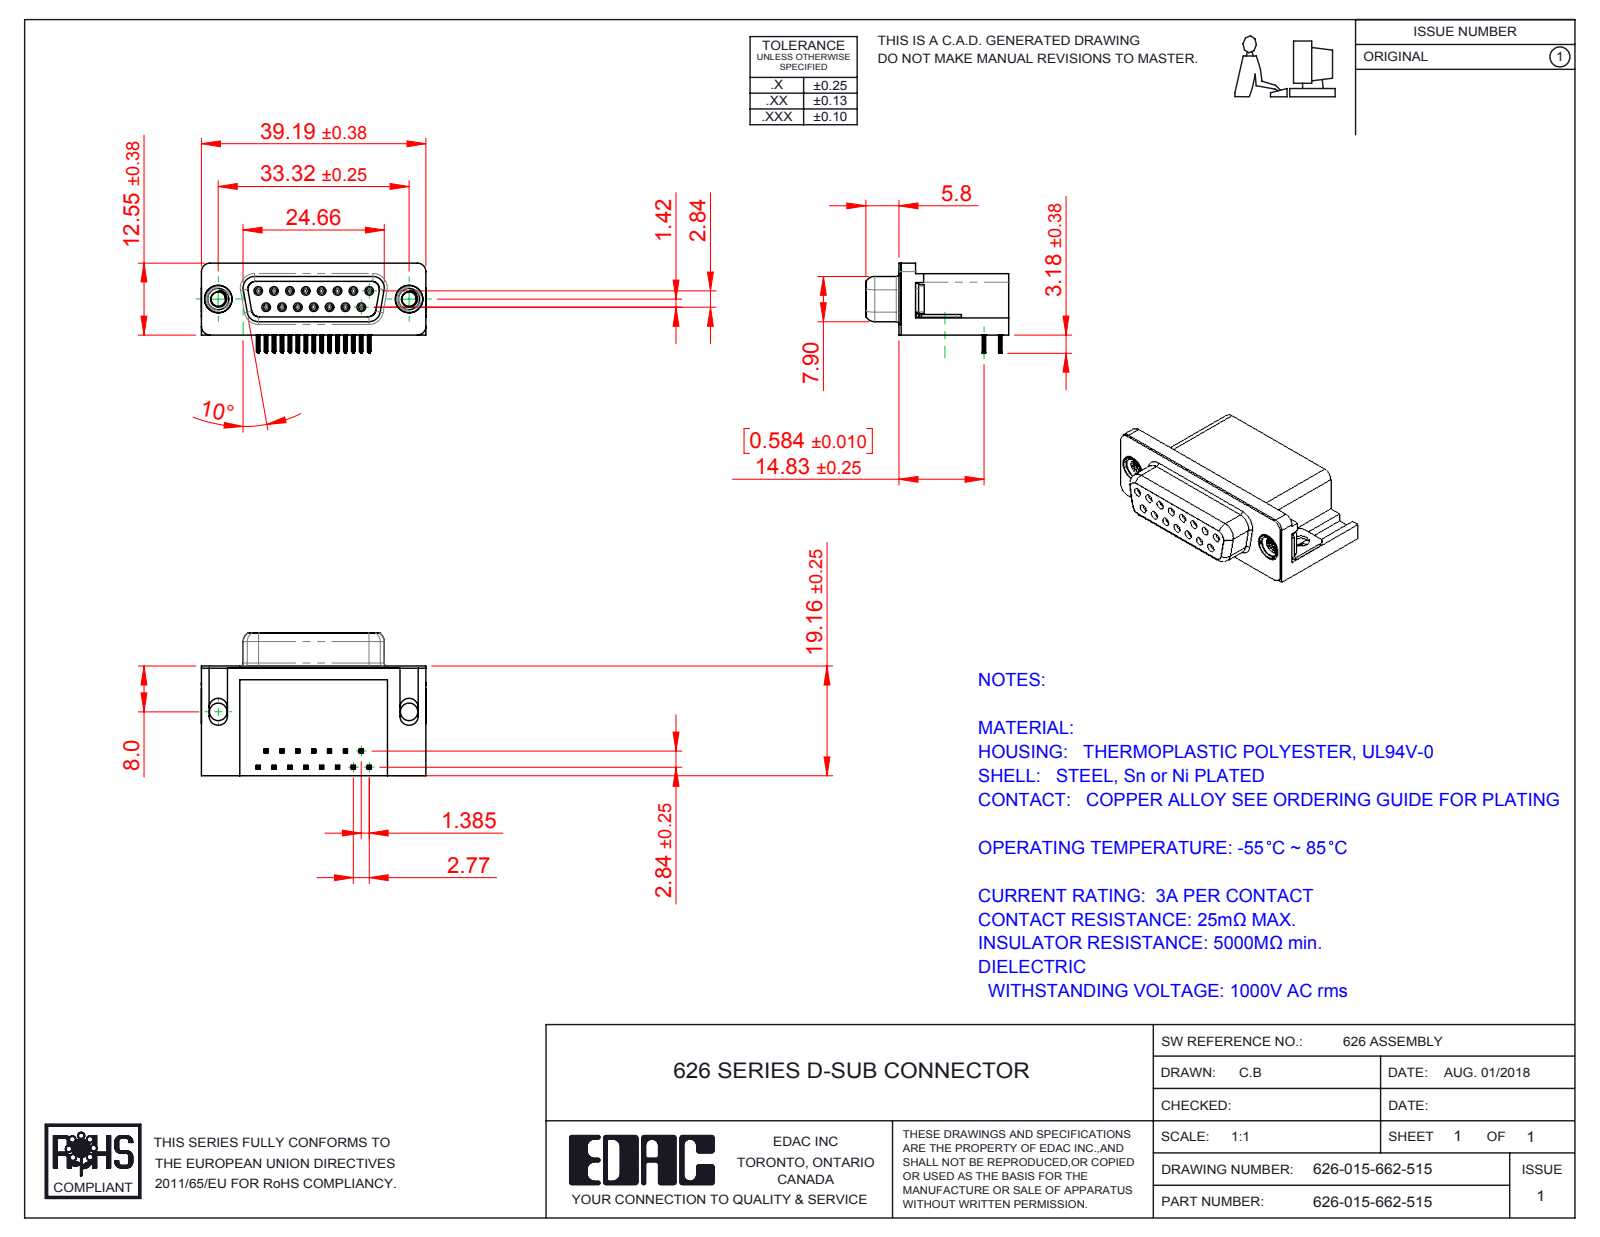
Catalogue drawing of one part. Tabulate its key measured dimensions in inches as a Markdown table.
| quantity | value |
| --- | --- |
| part name | 626 Contact Bottom; 626-015-662-515; 626 M3 Threaded Rivet; 626 Contact Top (+3 more) |
| STEP written by | SolidWorks 2016 (CONFIG_CONTROL_DESIGN) |
| units | inches |
| bodies | 21 solids, 2425 faces (1072 planar, 609 cylindrical, 744 other) |
| overall size | 1.544 × 0.983 × 0.619 |
| volume | 0.442 in³ |
| surface area | 12.43 in² |
| round holes (diameter × count) | 0.031 × 15, 0.035 × 15, 0.098 × 2, 0.12 × 2, 0.157 × 2, 0.189 × 2, 0.197 × 2 |
| round bosses / shafts (diameter × count) | 0.047 × 15, 0.193 × 2, 0.187 × 2, 0.154 × 2 |
| partial cylindrical surfaces (radius × count) | 0.004 × 120, 0.006 × 60, 0.014 × 30, 0.039 × 18, 0.013 × 15, 0.01 × 8, 0.053 × 8, 0.063 × 8 |
| main face-to-face distances | 0.016, 0.407, 0.014, 0.739, 0.107, 0.244, 0.754, 0.421, 0.369, 0.125 |
| hole center spacings | 0.124, 0.109, 0.218, 0.327, 0.436, 0.198, 0.198, 0.294 |
